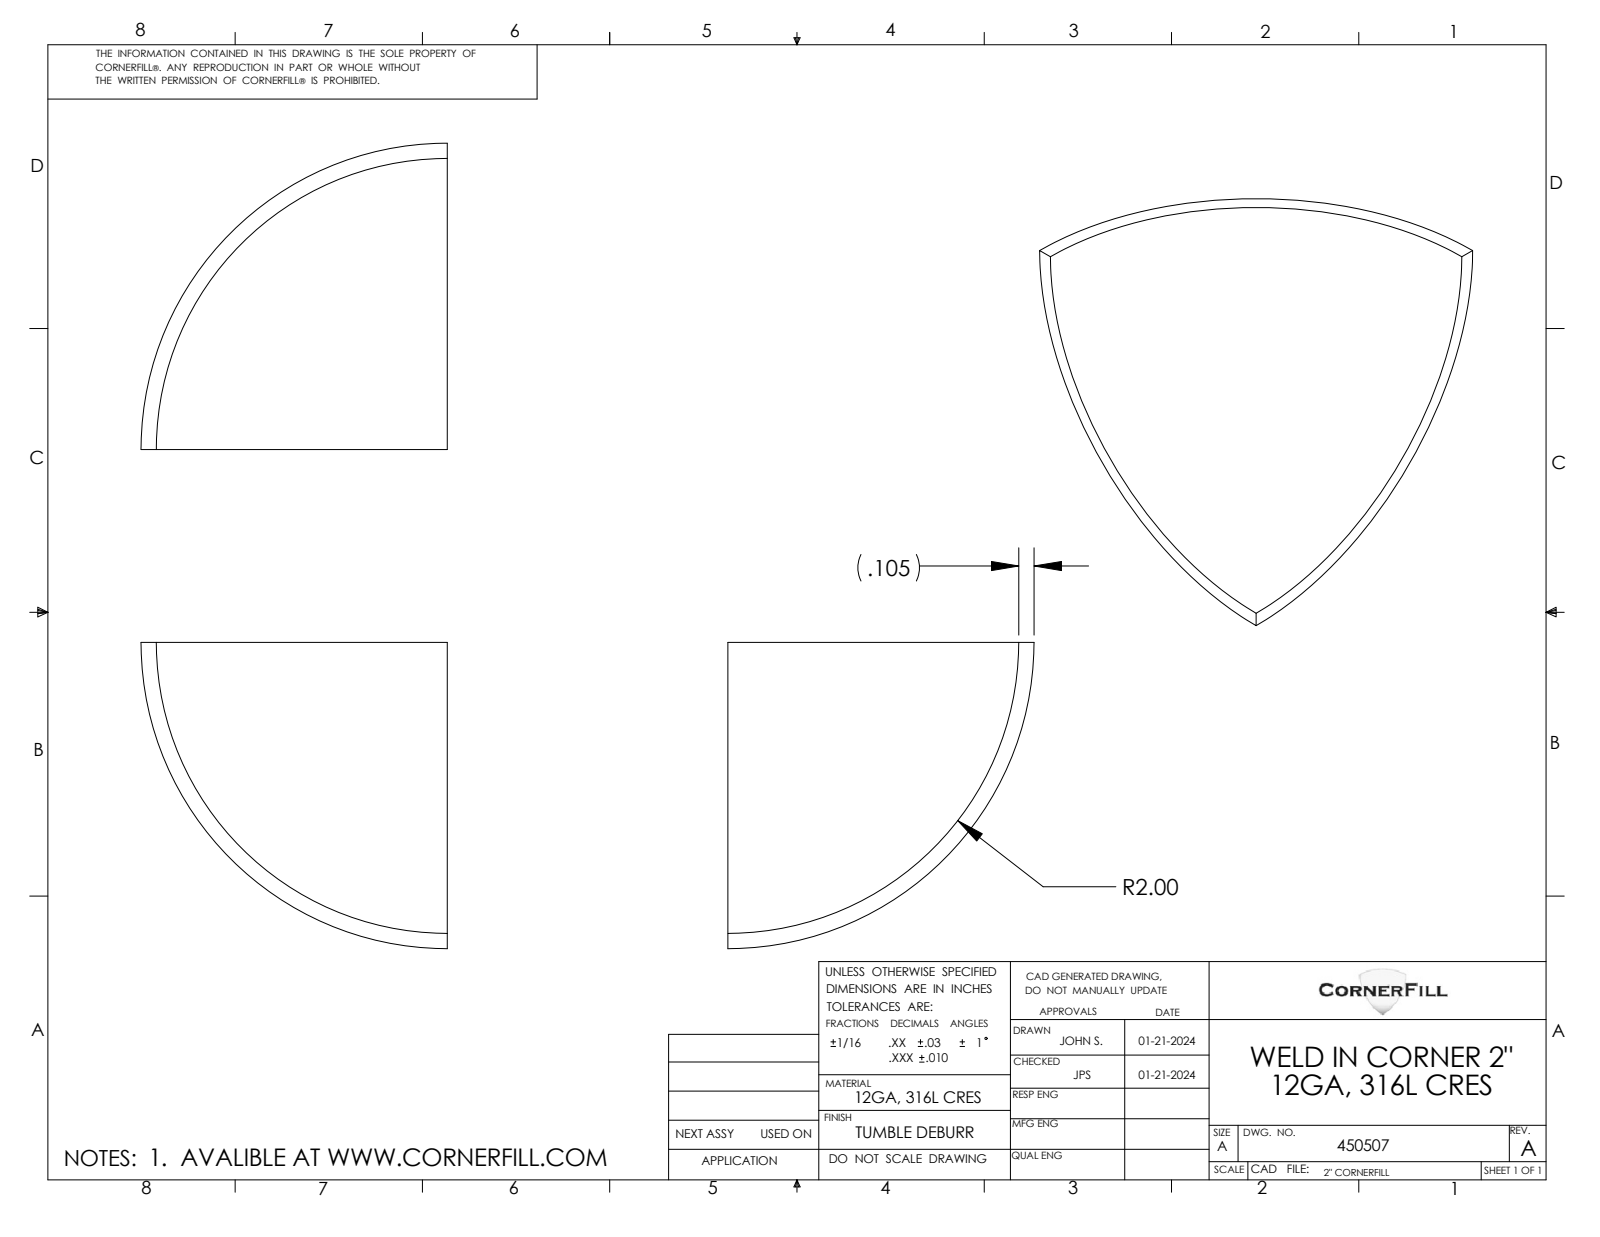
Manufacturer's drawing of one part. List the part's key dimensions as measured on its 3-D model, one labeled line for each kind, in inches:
Part name (STEP PRODUCT): 450507
STEP written by: SolidWorks 2021 (CONFIG_CONTROL_DESIGN)
Units: inches
Bodies: 1 solid, 5 faces (3 planar, 0 cylindrical, 2 other)
Overall size (bounding box): 2.977 × 2.105 × 2.105
Volume: 0.695 in³ · Surface area: 14.26 in²
